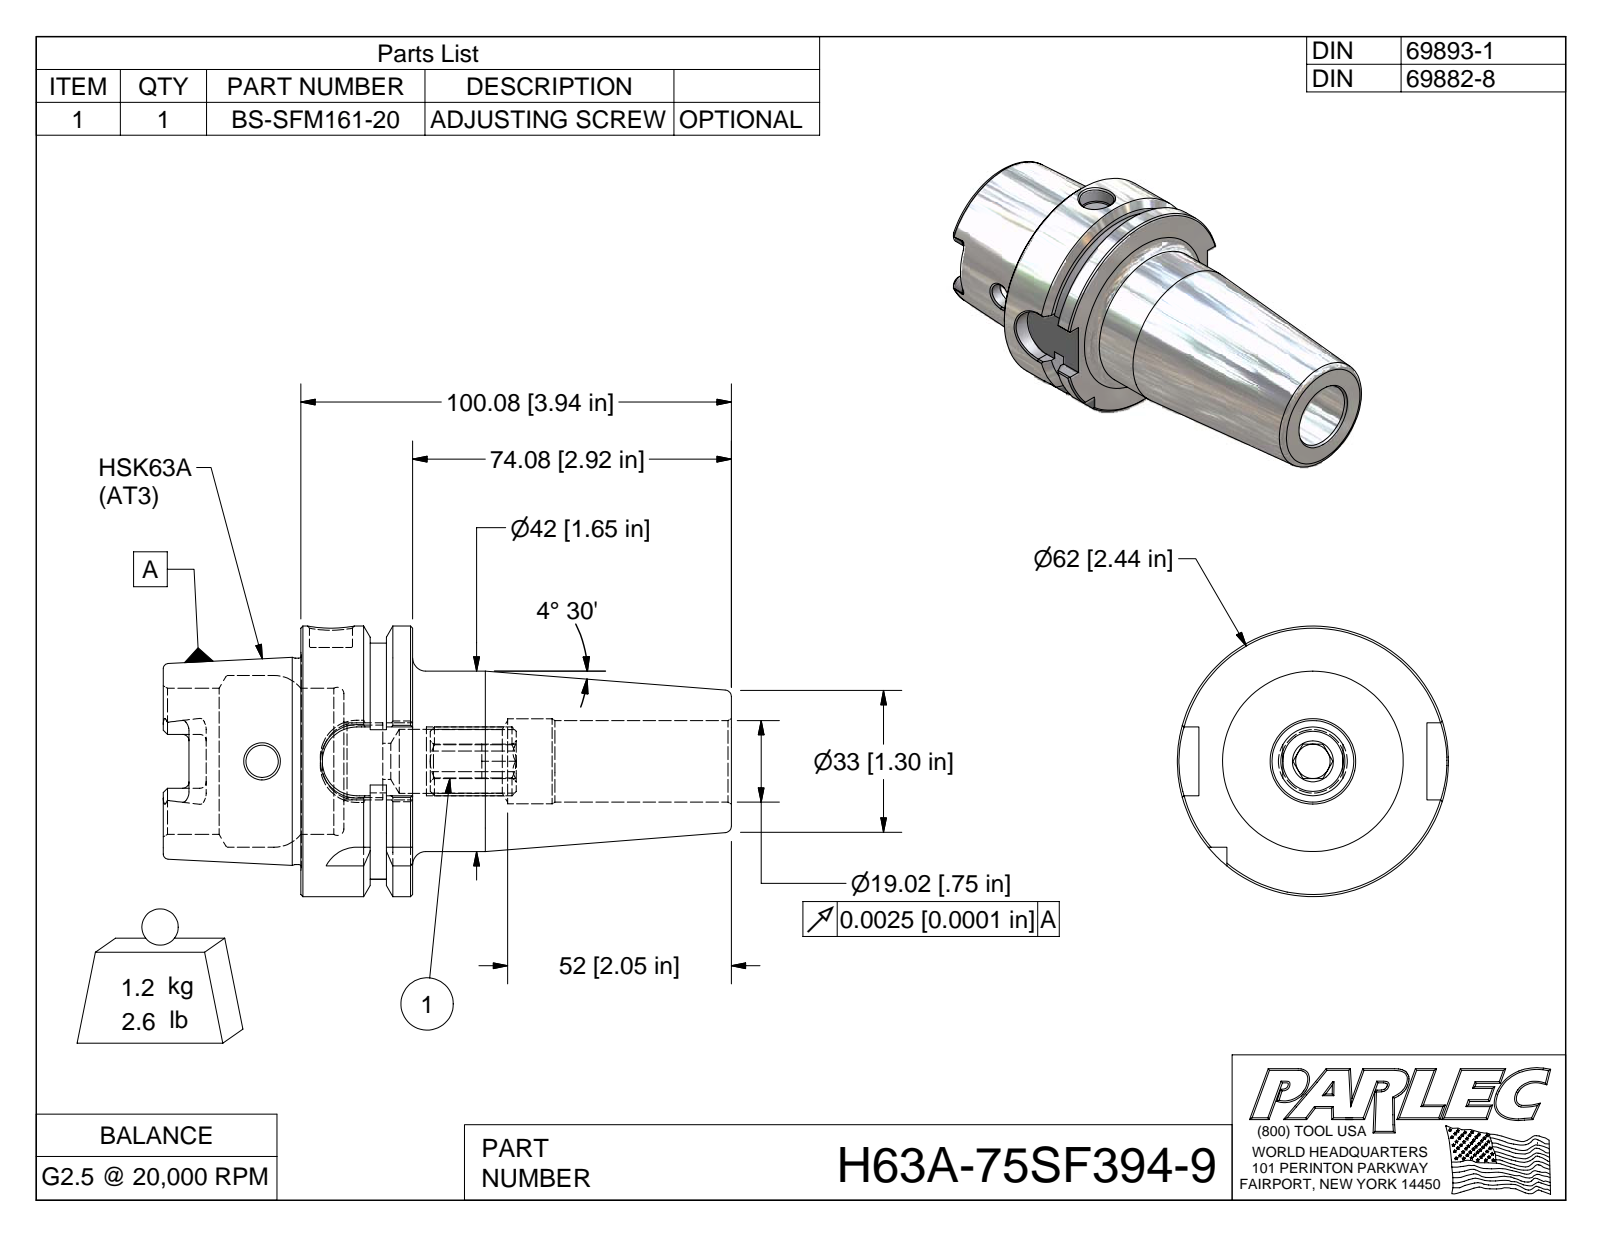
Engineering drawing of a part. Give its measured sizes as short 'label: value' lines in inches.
name: H63A-75SF394-9; H63A-75SF394-9-1; BS-SFM161-20
written by: Autodesk Inventor 2009 (AUTOMOTIVE_DESIGN)
unit: in
bodies: 2 solids, 157 faces (58 planar, 35 cylindrical, 64 other)
size: 5.2 × 2.48 × 2.48
volume: 9.28 in³; area: 56.46 in²
holes: 1× ⌀0.295, 1× ⌀0.394, 1× ⌀0.666, 1× ⌀0.749, 1× ⌀0.779, 1× ⌀1.339, 1× ⌀1.575
bosses: 1× ⌀2.48, 1× ⌀1.891, 1× ⌀1.654
rounds: 6× R0.059, 5× R0.315, 4× R0.113, 1× R1.083
face distances: 1.024, 0.241, 0.389, 0.394, 0.63, 1.26, 2.917, 3.94, 3.546, 2.283
